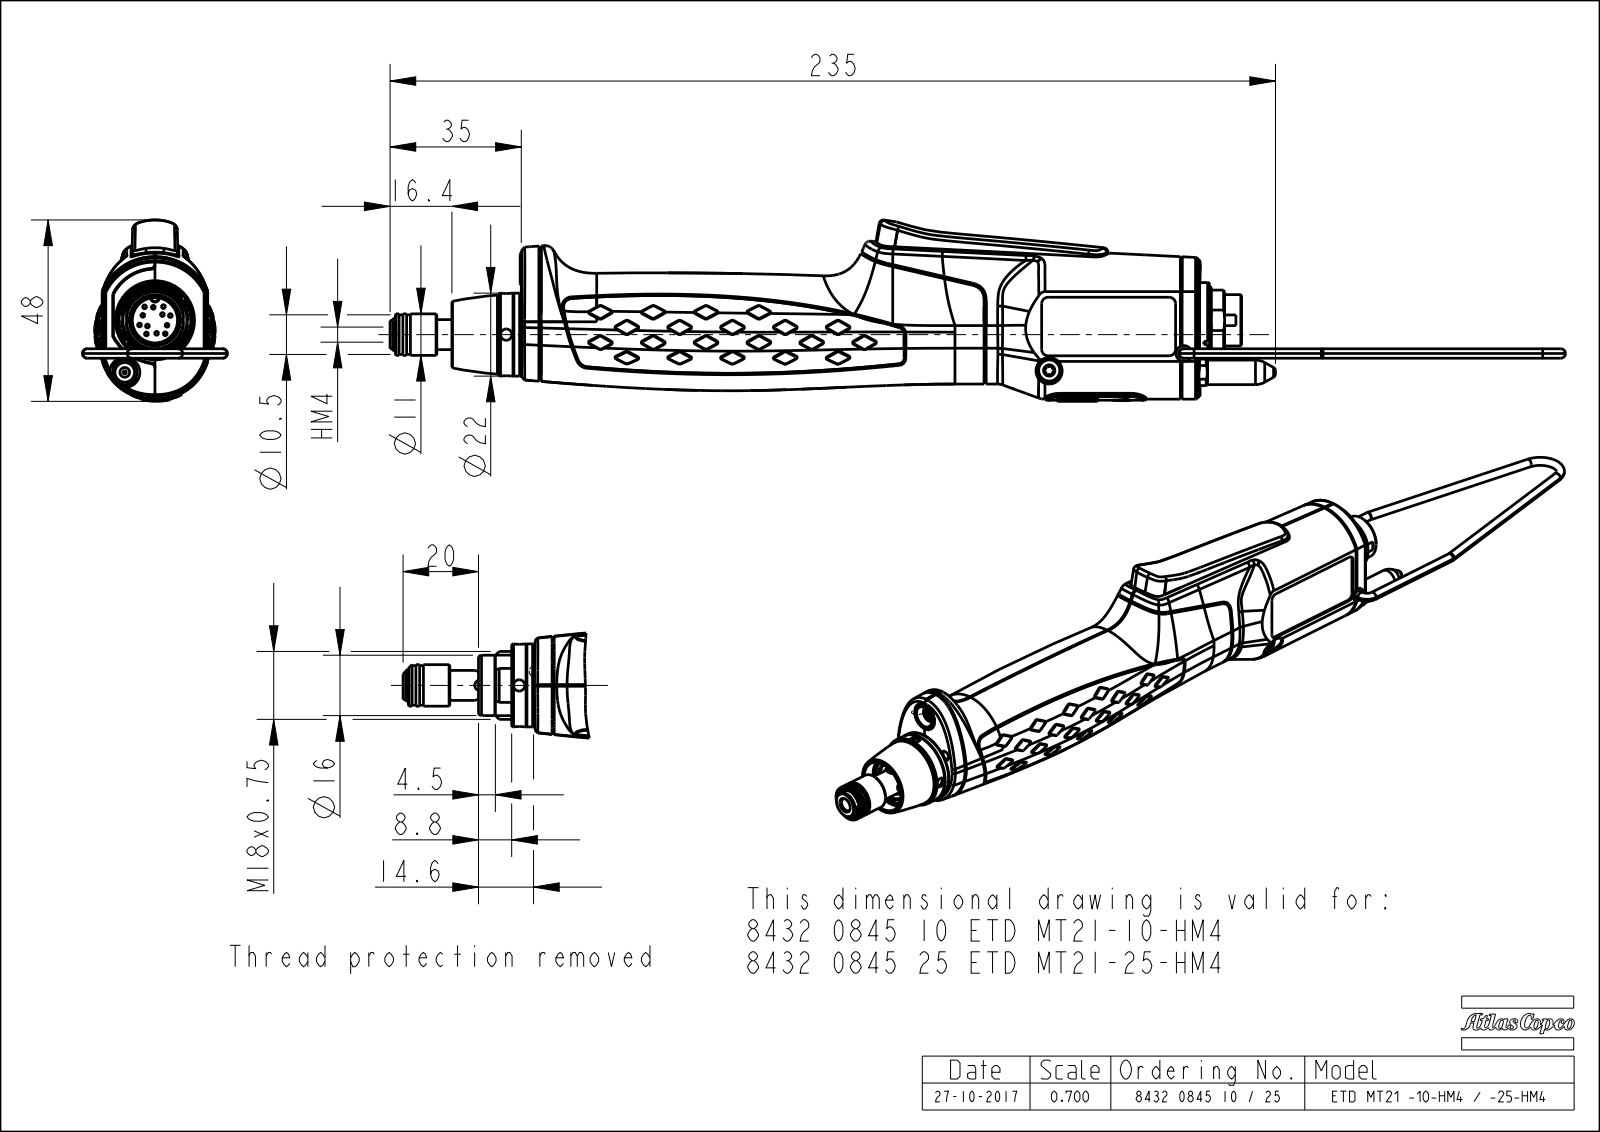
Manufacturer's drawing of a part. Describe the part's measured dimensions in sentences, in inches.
The part is named "4216289900; 4216290000; 4216289980_ASM; 0517110300 (+8 more)". Its 3-D file was written by "CREO PARAMETRIC BY PTC INC, 2016260 (CONFIG_CONTROL_DESIGN)". It is 22 solids with 3847 faces: 617 planar, 884 cylindrical and 2346 other. Overall it measures 12.272 by 1.893 by 1.512 inches. Its volume is 3.327 cubic inches and its surface area 95.96 square inches. Round holes: 3 of diameter 0.067, 3 of diameter 0.083, 3 of diameter 0.098, 3 of diameter 0.118, 2 of diameter 0.047, 2 of diameter 0.079, 2 of diameter 0.122, 2 of diameter 0.165, 2 of diameter 0.177, 2 of diameter 0.236, 2 of diameter 0.248, 2 of diameter 0.677. Round bosses or shafts: 12 of diameter 0.041, 12 of diameter 0.039, 12 of diameter 0.024, 1 of diameter 0.866, 1 of diameter 0.825, 1 of diameter 0.795, 1 of diameter 0.787, 1 of diameter 0.669. Partial cylindrical surfaces (rounded edges, fillets, slot ends): 247 of radius 0.012, 85 of radius 0.008, 41 of radius 0.004, 14 of radius 0.007, 13 of radius 0.02, 13 of radius 0.079, 10 of radius 0.157, 8 of radius 0.118. The main face-to-face distances are 0.059, 0.472, 0.531, 1.004, 0.079, 0.945, 0.02, 1.063, 0.551, 1.024. The hole center spacings are 0.15, 0.224, 0.369, 0.382, 0.443, 0.504, 0.535, 0.536.
